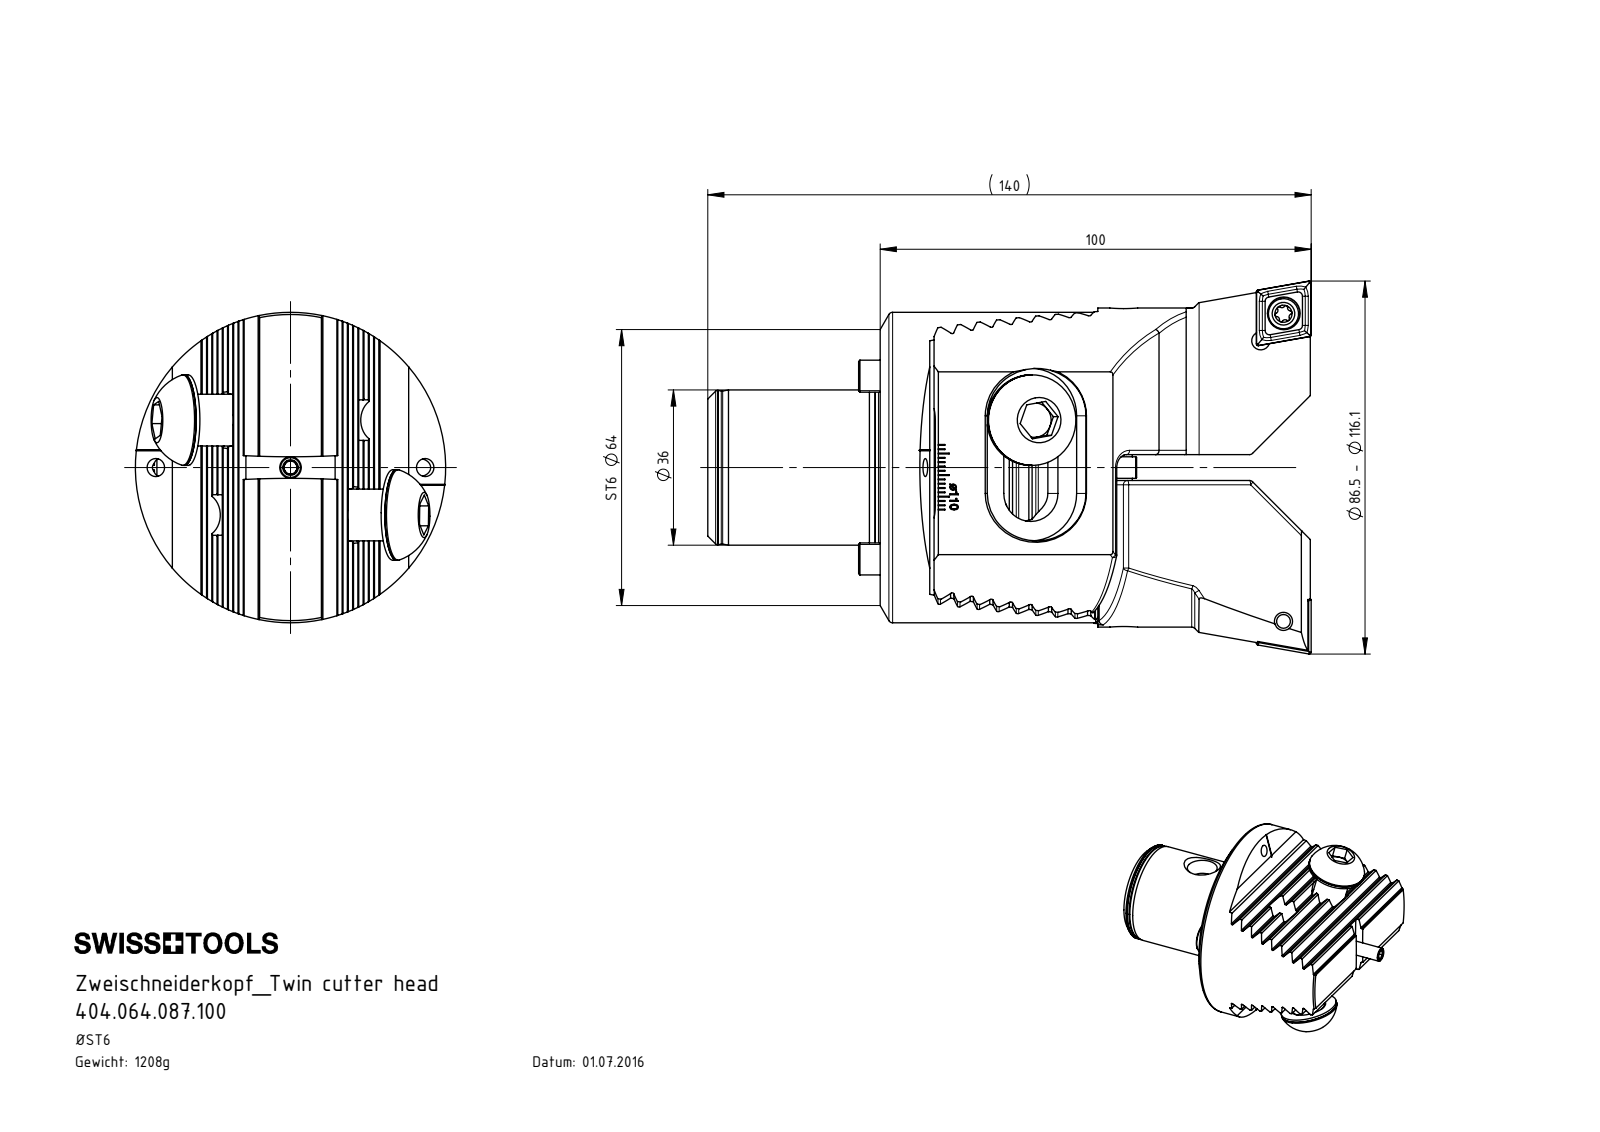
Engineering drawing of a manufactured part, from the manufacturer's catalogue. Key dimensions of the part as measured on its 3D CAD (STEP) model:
Part name (STEP PRODUCT): Z72-ER1.002.025_A; Z72-ER1.001.025; Z72-ER1.003.025_A_gespannt; ST6-Z72.K23.100_A (+3 more)
STEP written by: SolidWorks 2015 (CONFIG_CONTROL_DESIGN)
Units: millimetres
Bodies: 8 solids, 385 faces (157 planar, 114 cylindrical, 114 other)
Overall size (bounding box): 99.5 × 72 × 72
Volume: 153 534 mm³ · Surface area: 35 628 mm²
Round holes (diameter × count): ⌀5 ×5, ⌀10.25 ×2, ⌀13 ×2, ⌀13.5 ×2, ⌀3.3 ×1, ⌀8.5 ×1, ⌀16 ×1, ⌀19 ×1
Round bosses / shafts (diameter × count): ⌀21 ×2, ⌀12 ×2, ⌀72 ×1, ⌀36 ×1, ⌀35.8 ×1, ⌀35.3 ×1, ⌀5 ×1, ⌀4 ×1
Partial cylindrical surfaces — rounded edges, fillets, slot ends (radius × count): R0.34 ×18, R0.5 ×4, R5.47 ×2, R18.05 ×2, R220 ×2
Main face-to-face distances: 4.07, 8.14, 12.21, 20.36, 16.28, 16.29, 24.43, 12.22, 50.5, 28.5
Hole centre spacings: 21.5, 20.5, 43
